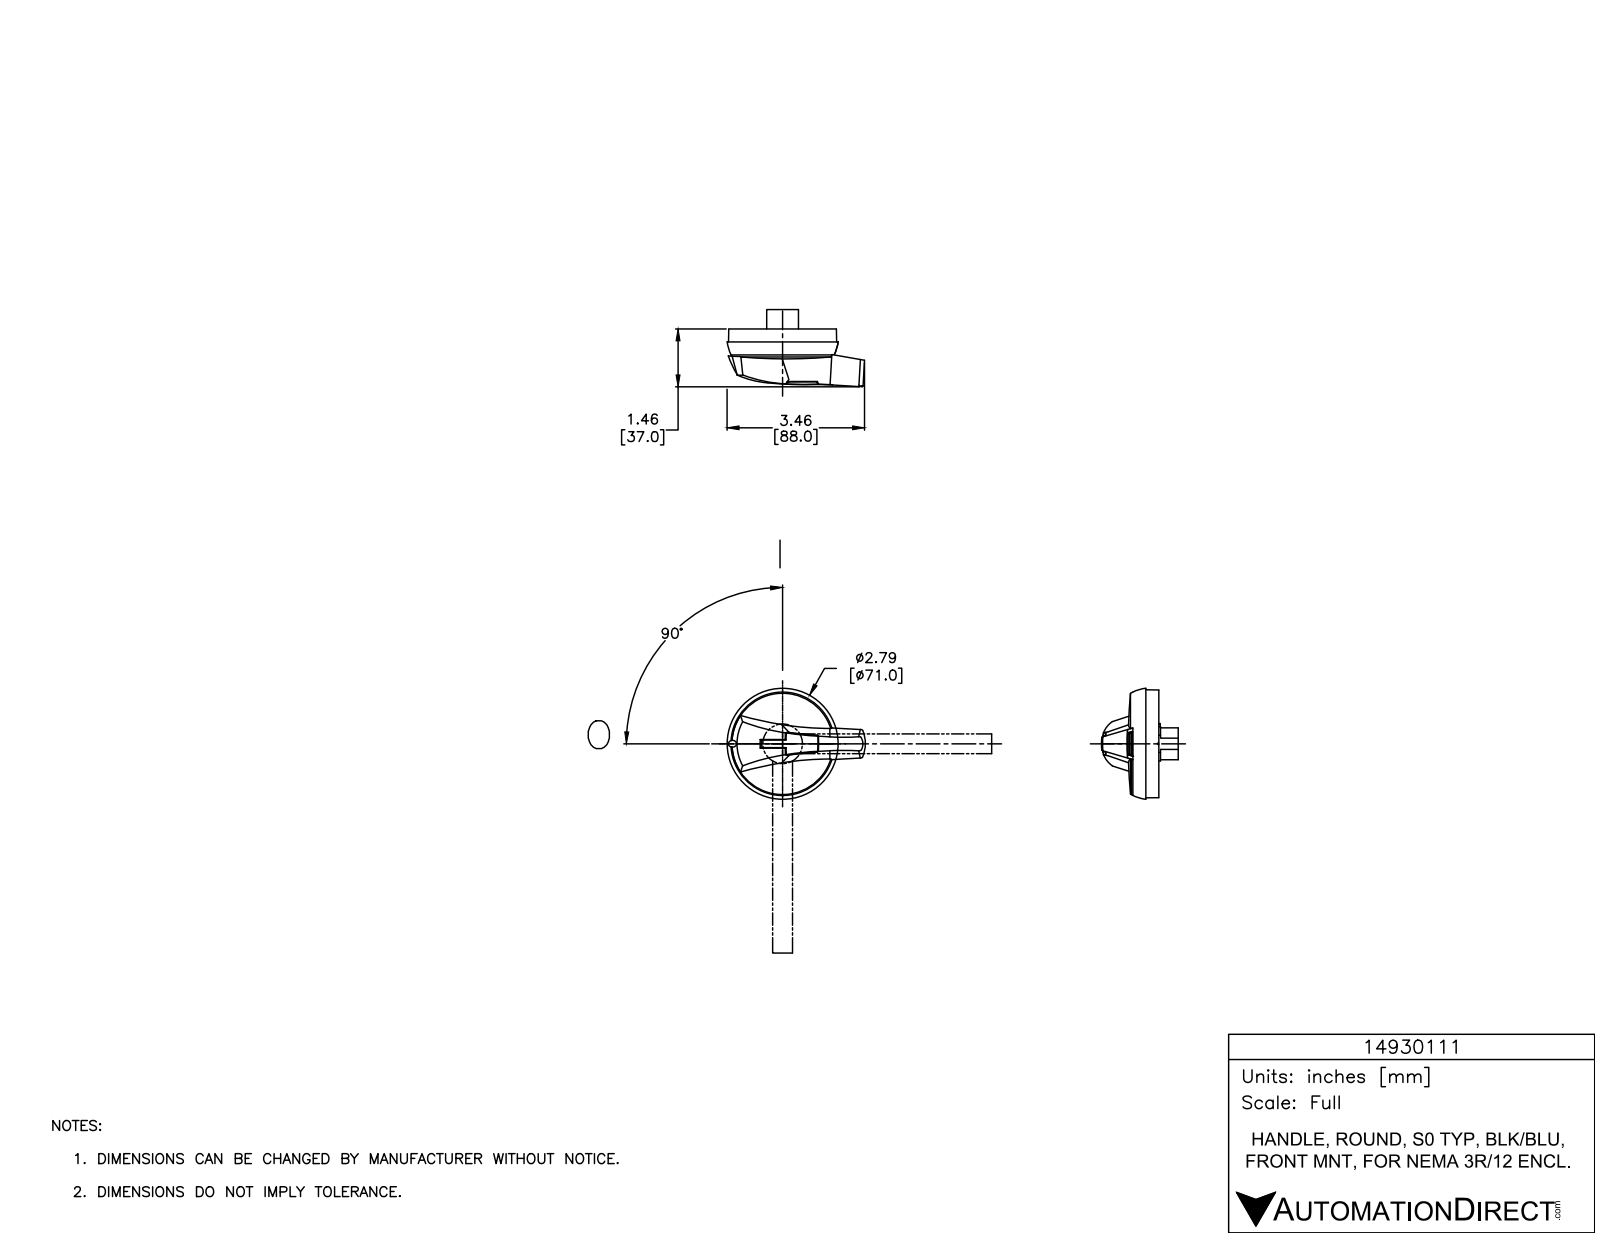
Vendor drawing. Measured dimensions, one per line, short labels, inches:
name: 14930111
written by: SolidWorks 2015 (AUTOMOTIVE_DESIGN)
unit: in
bodies: 6 solids, 2107 faces (458 planar, 370 cylindrical, 1279 other)
size: 3.479 × 2.8 × 1.925
volume: 3.472 in³; area: 93.06 in²
holes: 4× ⌀0.169, 4× ⌀0.193, 4× ⌀0.394, 3× ⌀0.079, 2× ⌀0.13, 2× ⌀0.157, 2× ⌀0.335, 1× ⌀0.118, 1× ⌀0.126, 1× ⌀0.457, 1× ⌀0.89, 1× ⌀2.618
bosses: 1× ⌀2.559, 1× ⌀0.984
rounds: 114× R0.02, 23× R0.039, 19× R0.01, 10× R0.012, 8× R0.03, 6× R0.641, 4× R0.142, 4× R0.187
face distances: 0.059, 0.071, 0.13, 0.616, 0.053, 0.03, 0.557, 0.486, 0.152, 0.295
hole spacings: 0.564, 0.961, 1.557, 1.181, 0.669, 0.677, 0.844, 1.102
